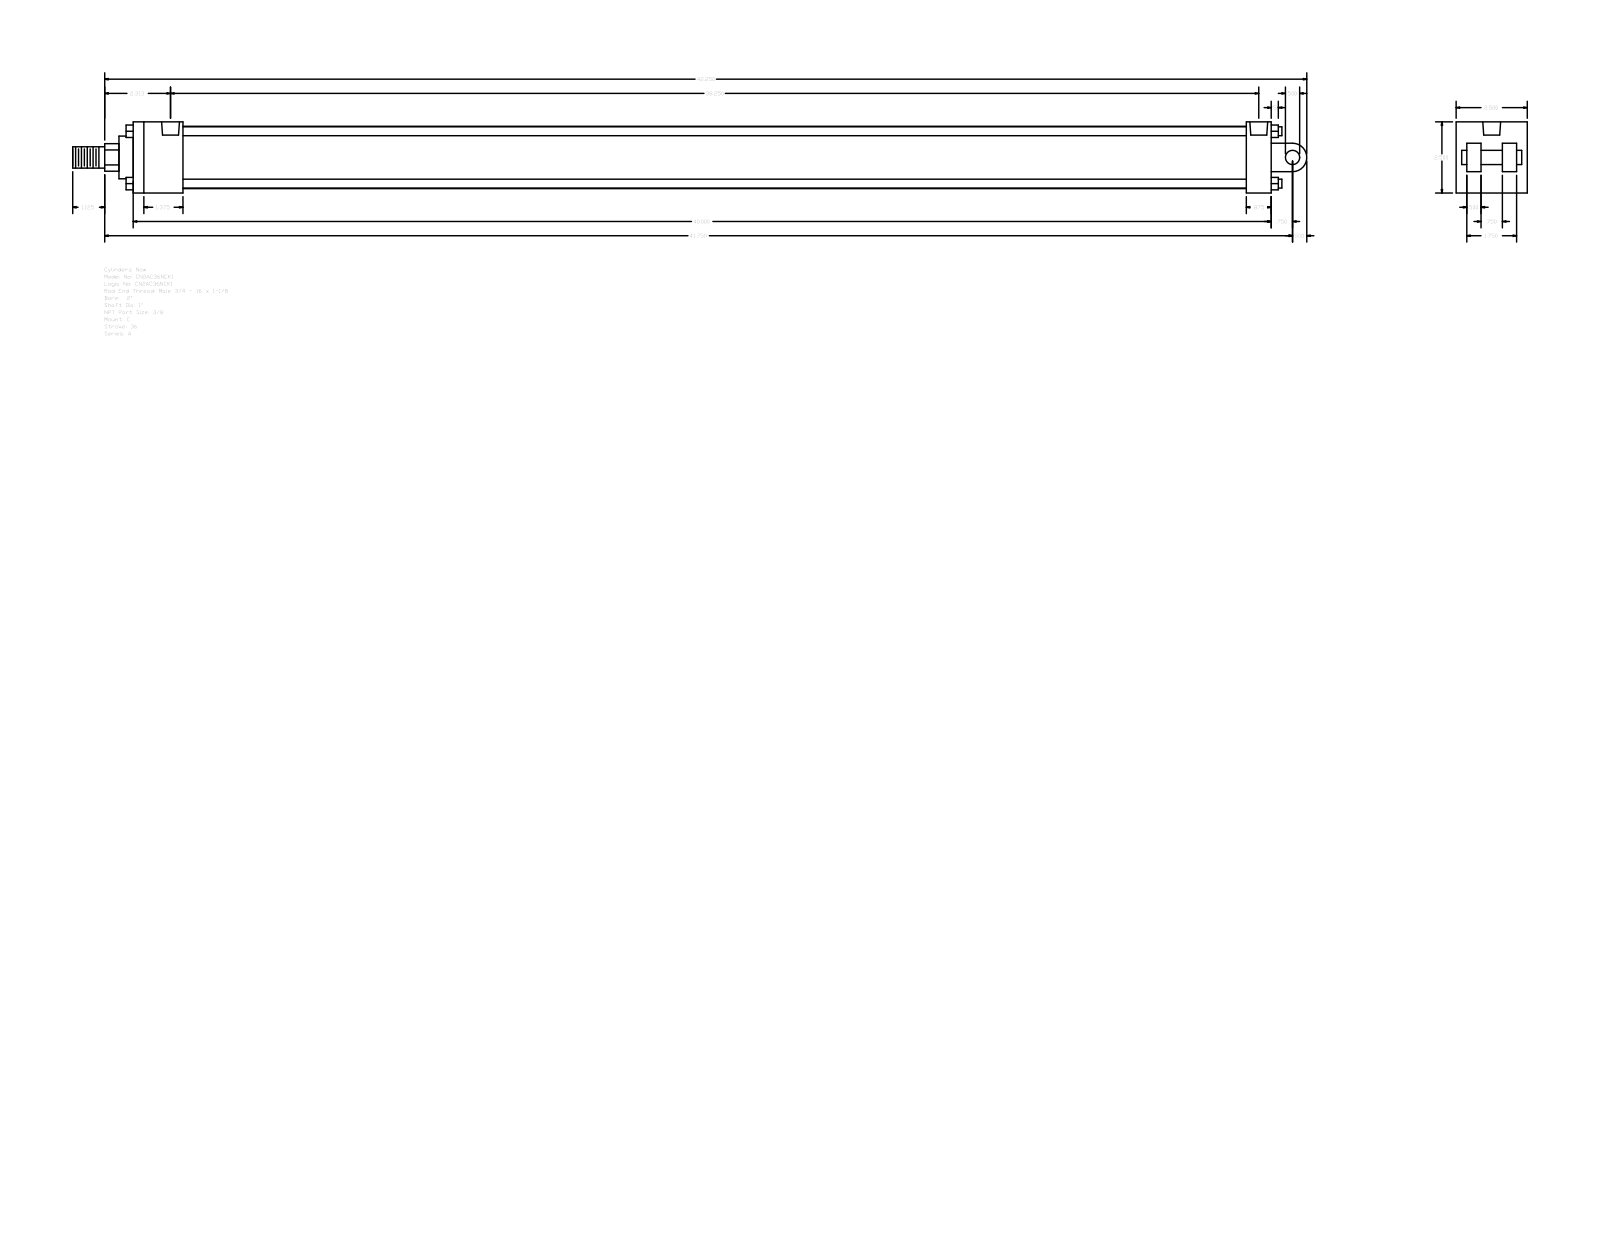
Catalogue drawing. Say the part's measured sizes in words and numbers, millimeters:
The part is named "A_C__0200_1". Its 3-D file was written by "GSSL Pune (CONFIG_CONTROL_DESIGN)". It is 0 solids with 135 faces: 102 planar, 33 cylindrical and 0 other. Overall it measures 1101.72 by 63.5 by 63.5 millimeters. Round holes: 4 of diameter 5.56, 2 of diameter 15.93. Round bosses or shafts: 4 of diameter 7.94, 1 of diameter 55.63, 1 of diameter 38.1, 1 of diameter 25.4, 1 of diameter 19.05, 1 of diameter 12.7. Partial cylindrical surfaces (rounded edges, fillets, slot ends): 1 of radius 12.29, 1 of radius 12.7. The main face-to-face distances are 63.5, 1016, 44.45, 12.7, 9.52, 971.55, 993.77, 949.32, 22.23, 53.98. The hole center spacings are 965.98, 1.59, 3.98, 967.57, 969.96, 971.55.
